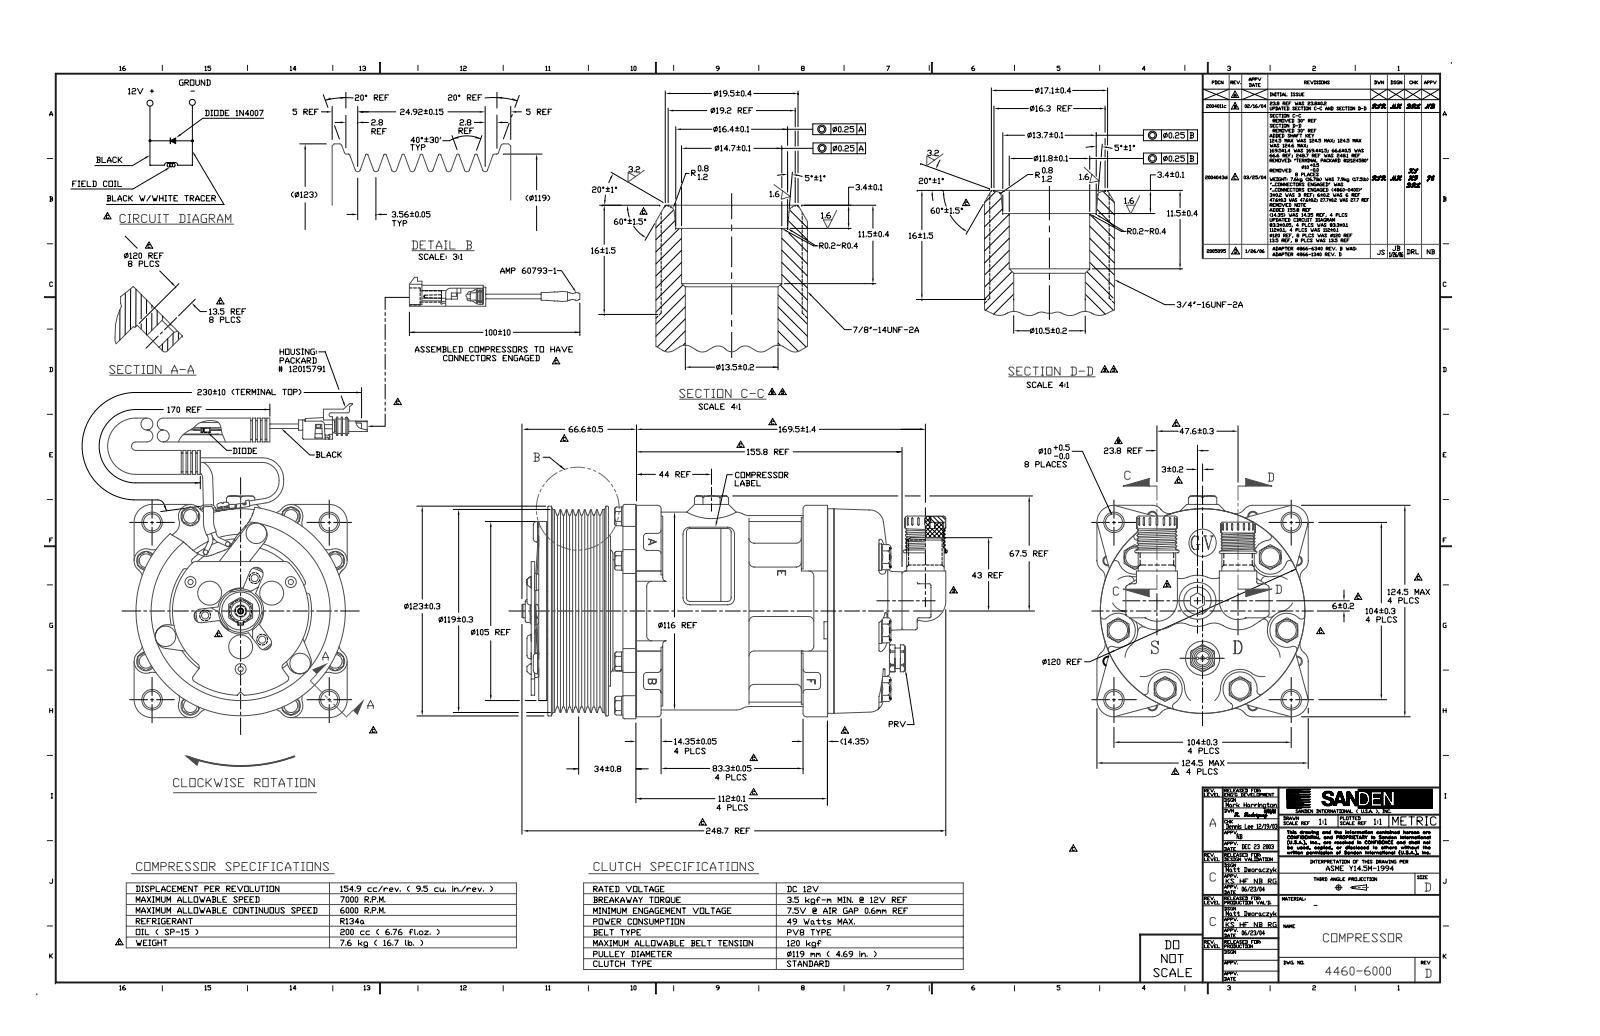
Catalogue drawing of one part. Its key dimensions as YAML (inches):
part_name: "SANDEN_4460_REV_D_COMPR_AC1"
step_written_by: "SolidWorks 2010 (CONFIG_CONTROL_DESIGN)"
units: inches
bodies: {solids: 3, faces: 2917, planar: 788, cylindrical: 790, other: 1339}
overall_size: [16.981, 9.783, 4.921]
volume: 135.4
surface_area: 424.6
round_holes:
  - {diameter: 0.217, count: 8}
  - {diameter: 0.276, count: 8}
  - {diameter: 0.335, count: 8}
  - {diameter: 0.469, count: 6}
  - {diameter: 0.315, count: 4}
  - {diameter: 0.404, count: 4}
  - {diameter: 0.087, count: 3}
  - {diameter: 0.2, count: 3}
  - {diameter: 0.26, count: 3}
  - {diameter: 0.413, count: 3}
  - {diameter: 0.531, count: 2}
  - {diameter: 1.078, count: 2}
round_bosses_or_shafts:
  - {diameter: 0.508, count: 8}
  - {diameter: 0.224, count: 8}
  - {diameter: 0.602, count: 6}
  - {diameter: 0.106, count: 6}
  - {diameter: 0.472, count: 4}
  - {diameter: 0.394, count: 4}
  - {diameter: 0.551, count: 3}
  - {diameter: 0.311, count: 3}
partial_cylinders:
  - {radius: 0.039, count: 60}
  - {radius: 0.276, count: 33}
  - {radius: 0.079, count: 31}
  - {radius: 0.256, count: 25}
  - {radius: 0.118, count: 24}
  - {radius: 0.197, count: 19}
  - {radius: 0.157, count: 13}
  - {radius: 0.059, count: 12}
face_to_face_distances: [0.079, 1.832, 1.77, 1.99, 0.22, 0.252, 1.517, 1.738, 3.844, 0.565]
hole_center_spacings: [0.896, 2.474, 3.212, 4.324, 5.311, 2.895, 3.5, 4.094]
